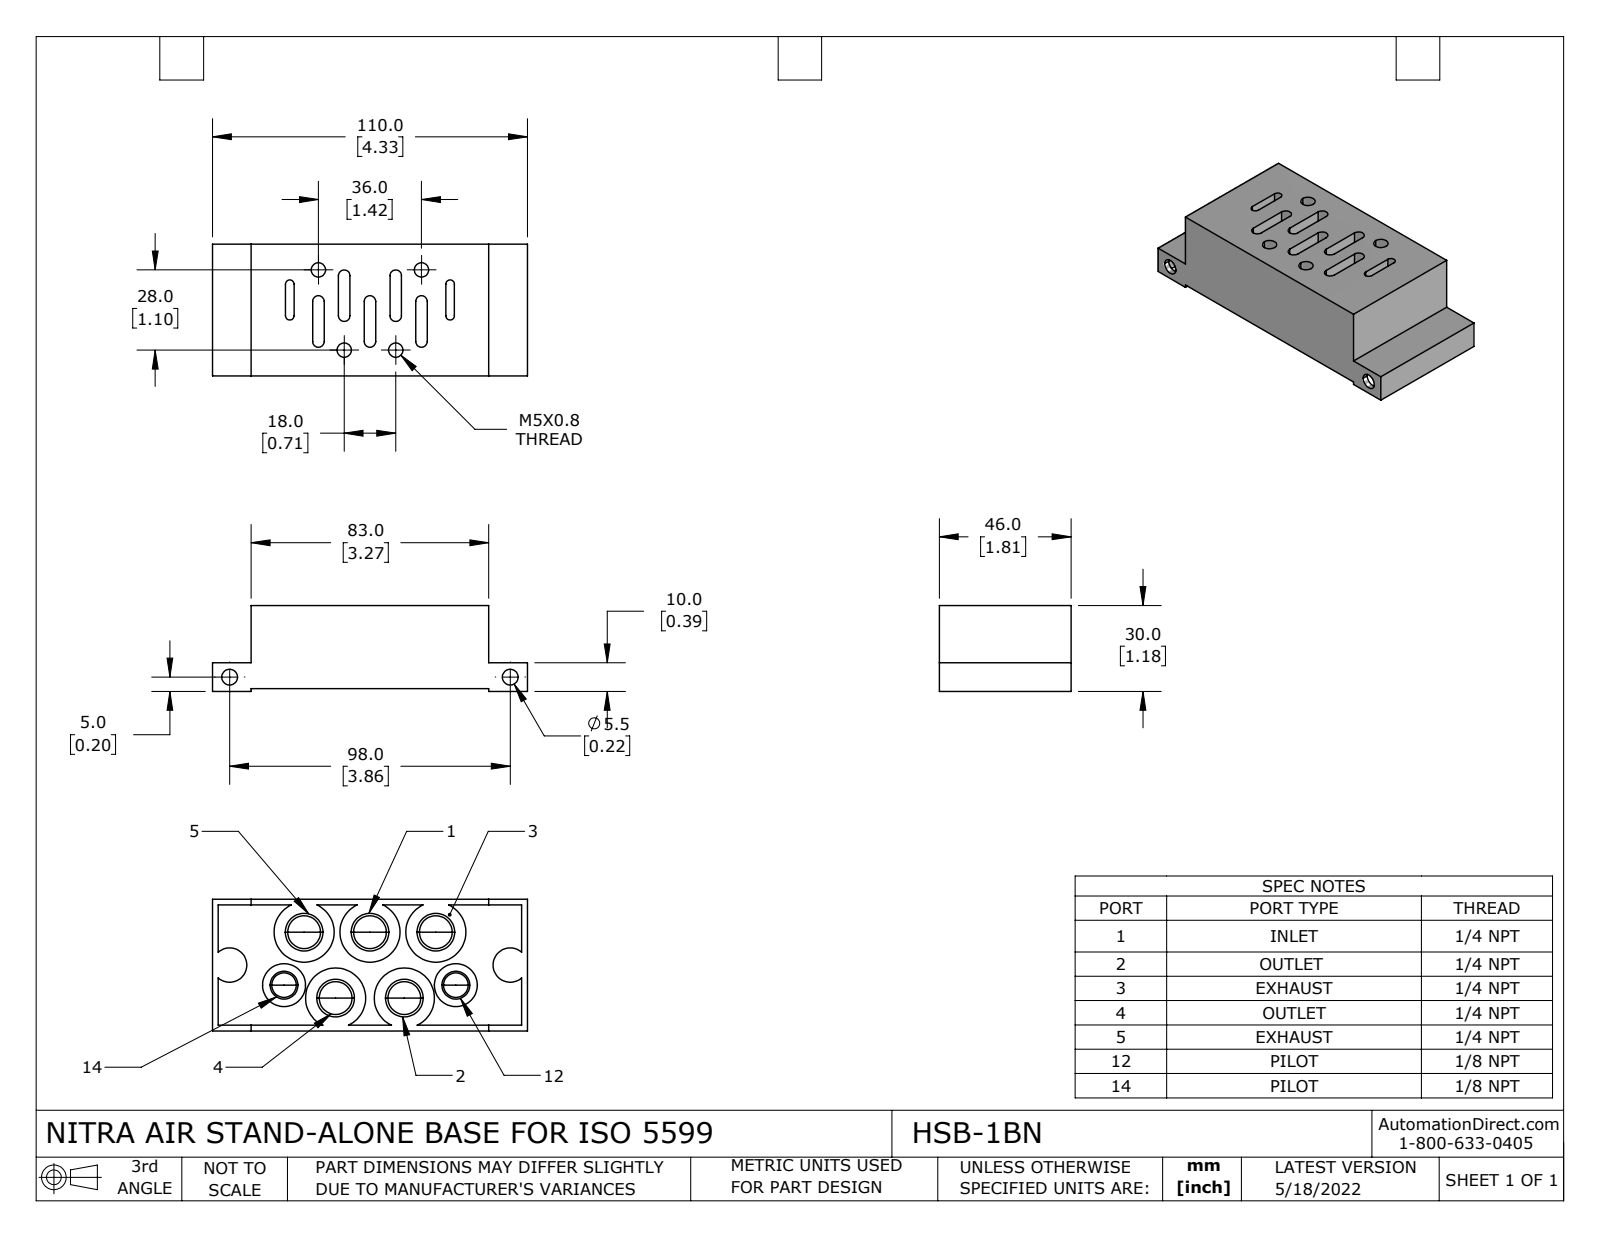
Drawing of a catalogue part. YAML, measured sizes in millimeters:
part_name: "HSB-1BN"
step_written_by: "SolidWorks 2021 (CONFIG_CONTROL_DESIGN)"
units: millimeters
bodies: {solids: 1, faces: 143, planar: 56, cylindrical: 59, other: 28}
overall_size: [110, 46, 30]
volume: 97492
surface_area: 27105
round_holes:
  - {diameter: 11.45, count: 5}
  - {diameter: 5, count: 4}
  - {diameter: 5.5, count: 2}
  - {diameter: 8.57, count: 2}
round_bosses_or_shafts:
  - {diameter: 21, count: 5}
  - {diameter: 15, count: 2}
partial_cylinders:
  - {radius: 2, count: 10}
  - {radius: 1.5, count: 4}
  - {radius: 6, count: 2}
face_to_face_distances: [2, 46, 22, 9, 7, 29, 44, 20, 13.5, 83]
hole_center_spacings: [6.5, 9.34, 13.89, 14.22, 18.55, 19.78, 23, 25.5]
